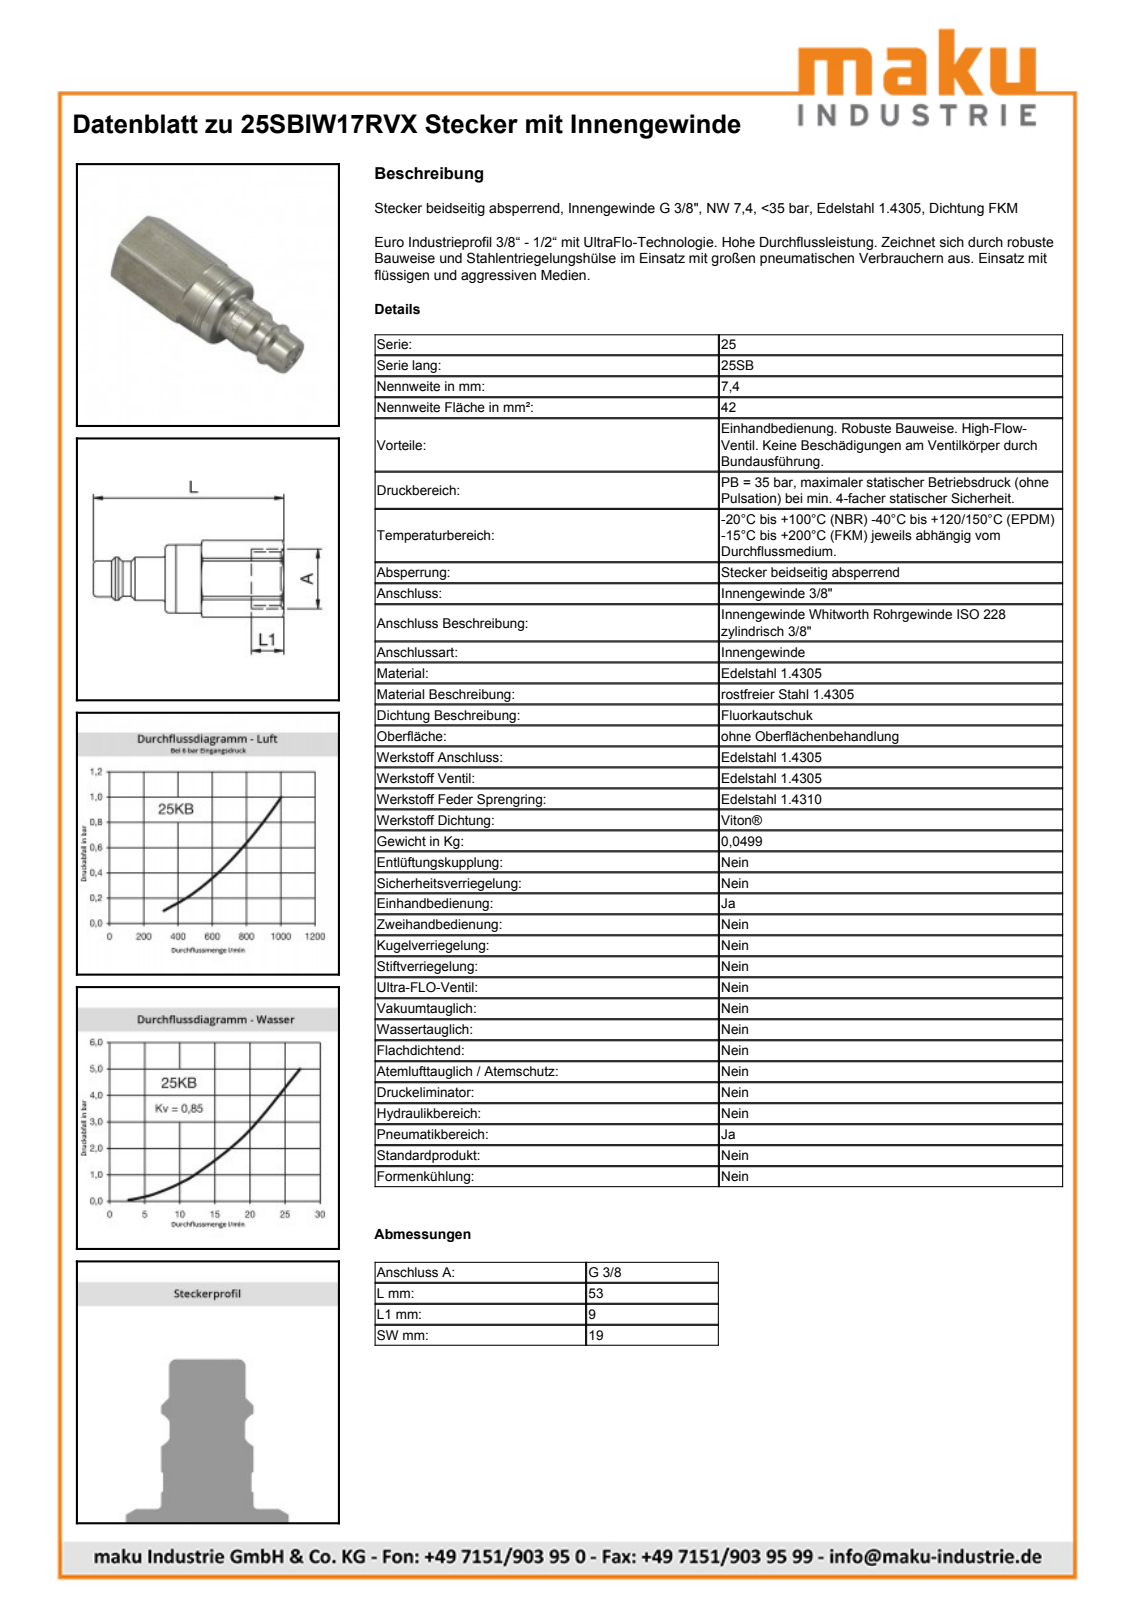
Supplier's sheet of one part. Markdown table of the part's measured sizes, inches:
| quantity | value |
| --- | --- |
| part name | D111969 |
| STEP written by | Autodesk Inventor 2013 (AUTOMOTIVE_DESIGN) |
| units | inches |
| bodies | 1 solid, 48 faces (12 planar, 16 cylindrical, 20 other) |
| overall size | 2.205 × 0.843 × 0.748 |
| volume | 0.78 in³ |
| surface area | 5.857 in² |
| round holes (diameter × count) | 0.63 × 1 |
| round bosses / shafts (diameter × count) | 0.748 × 1, 0.746 × 1, 0.571 × 1, 0.472 × 1, 0.39 × 1, 0.384 × 1 |
| partial cylindrical surfaces (radius × count) | 0.421 × 1 |
| main face-to-face distances | 0.748, 1.417, 0.787, 2.205, 0.906, 0.118, 1.299, 0.965, 0.177, 0.059 |
